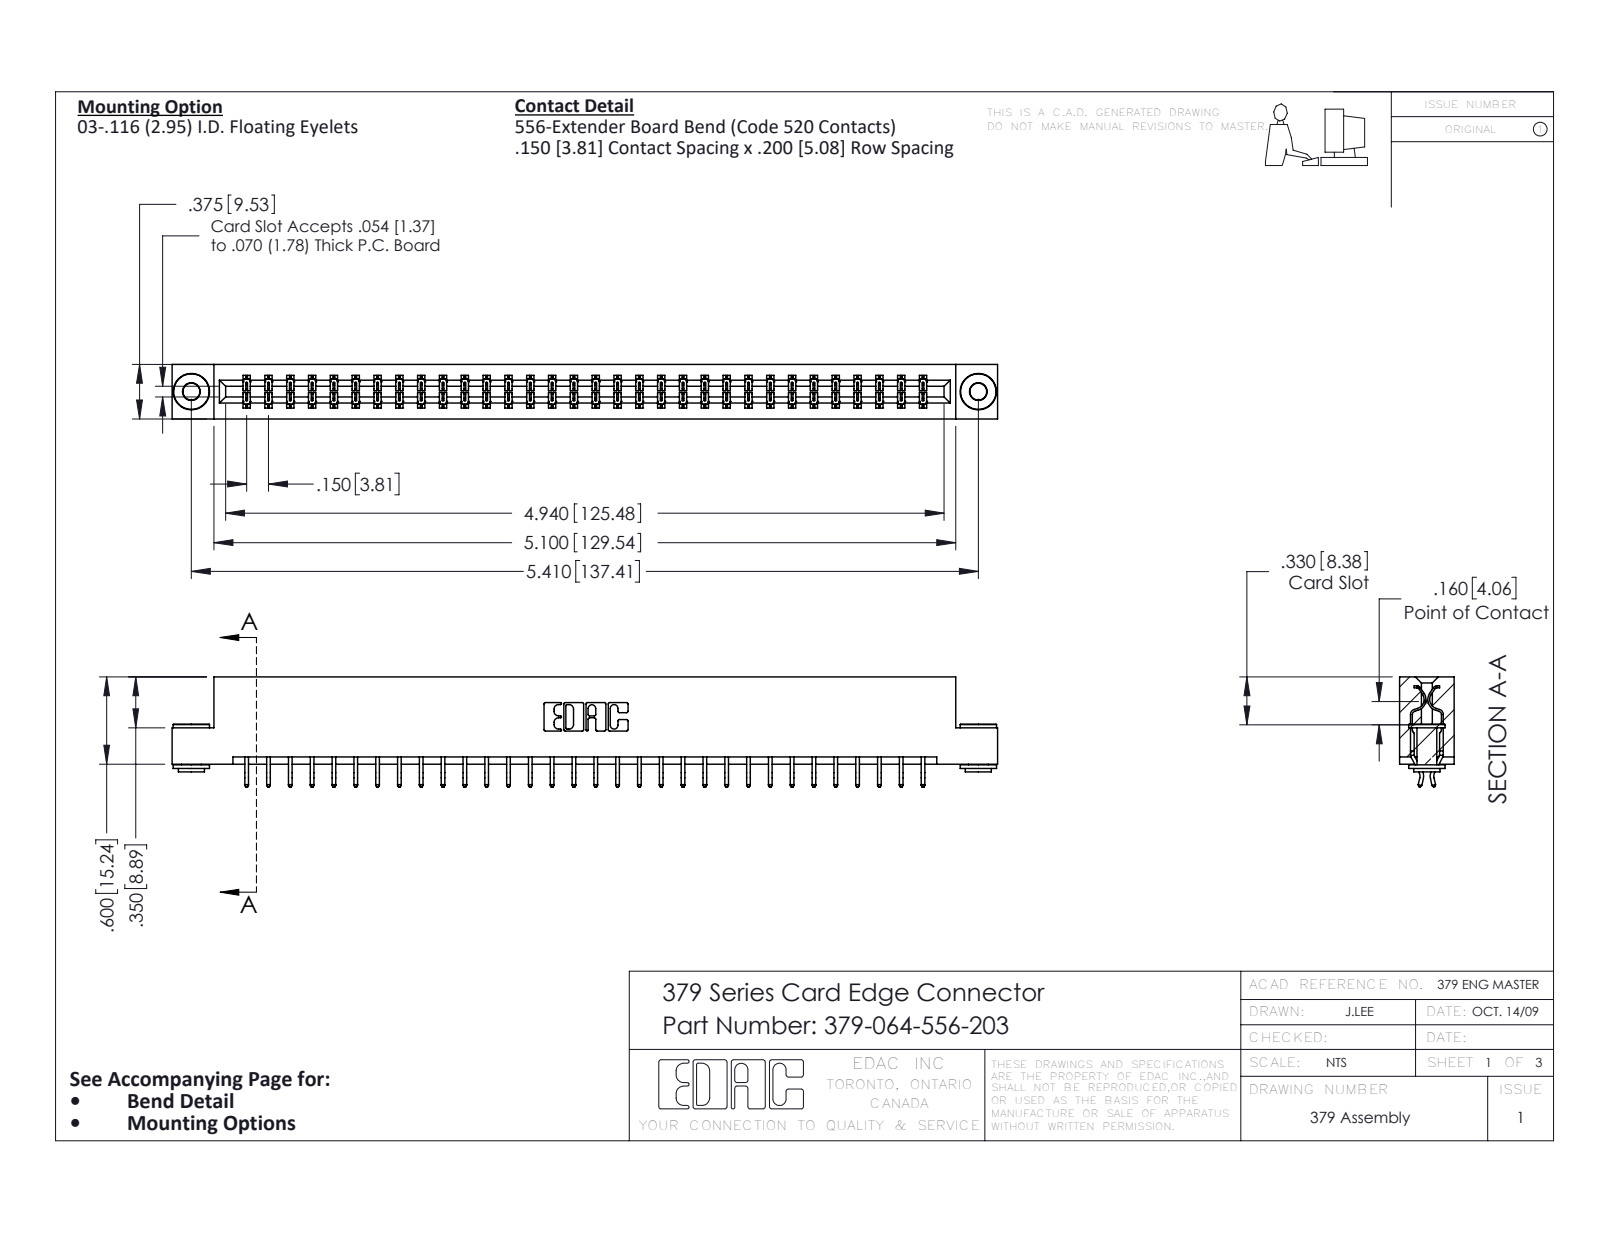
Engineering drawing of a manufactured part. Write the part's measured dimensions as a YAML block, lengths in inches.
part_name: "379 Part_Flush - .156 Dia - TH; 345-250-002_345-250-002-102; 345-292-001_556 Tail; 379-064-556-203"
step_written_by: "SolidWorks 2016 (CONFIG_CONTROL_DESIGN)"
units: inches
bodies: {solids: 67, faces: 3864, planar: 2640, cylindrical: 1216, other: 8}
overall_size: [5.675, 0.757, 0.375]
volume: 0.931
surface_area: 26.65
round_holes:
  - {diameter: 0.116, count: 2}
  - {diameter: 0.156, count: 2}
round_bosses_or_shafts:
  - {diameter: 0.25, count: 2}
  - {diameter: 0.18, count: 2}
  - {diameter: 0.136, count: 2}
partial_cylinders:
  - {radius: 0.006, count: 96}
  - {radius: 0.01, count: 22}
  - {radius: 0.007, count: 6}
  - {radius: 0.031, count: 6}
  - {radius: 0.026, count: 3}
  - {radius: 0.01, count: 2}
  - {radius: 0.014, count: 2}
  - {radius: 0.022, count: 2}
face_to_face_distances: [0.3, 0.075, 0.375, 0.2, 0.225, 0.1, 0.15, 0.076, 0.55, 0.275]
hole_center_spacings: [5.41]
